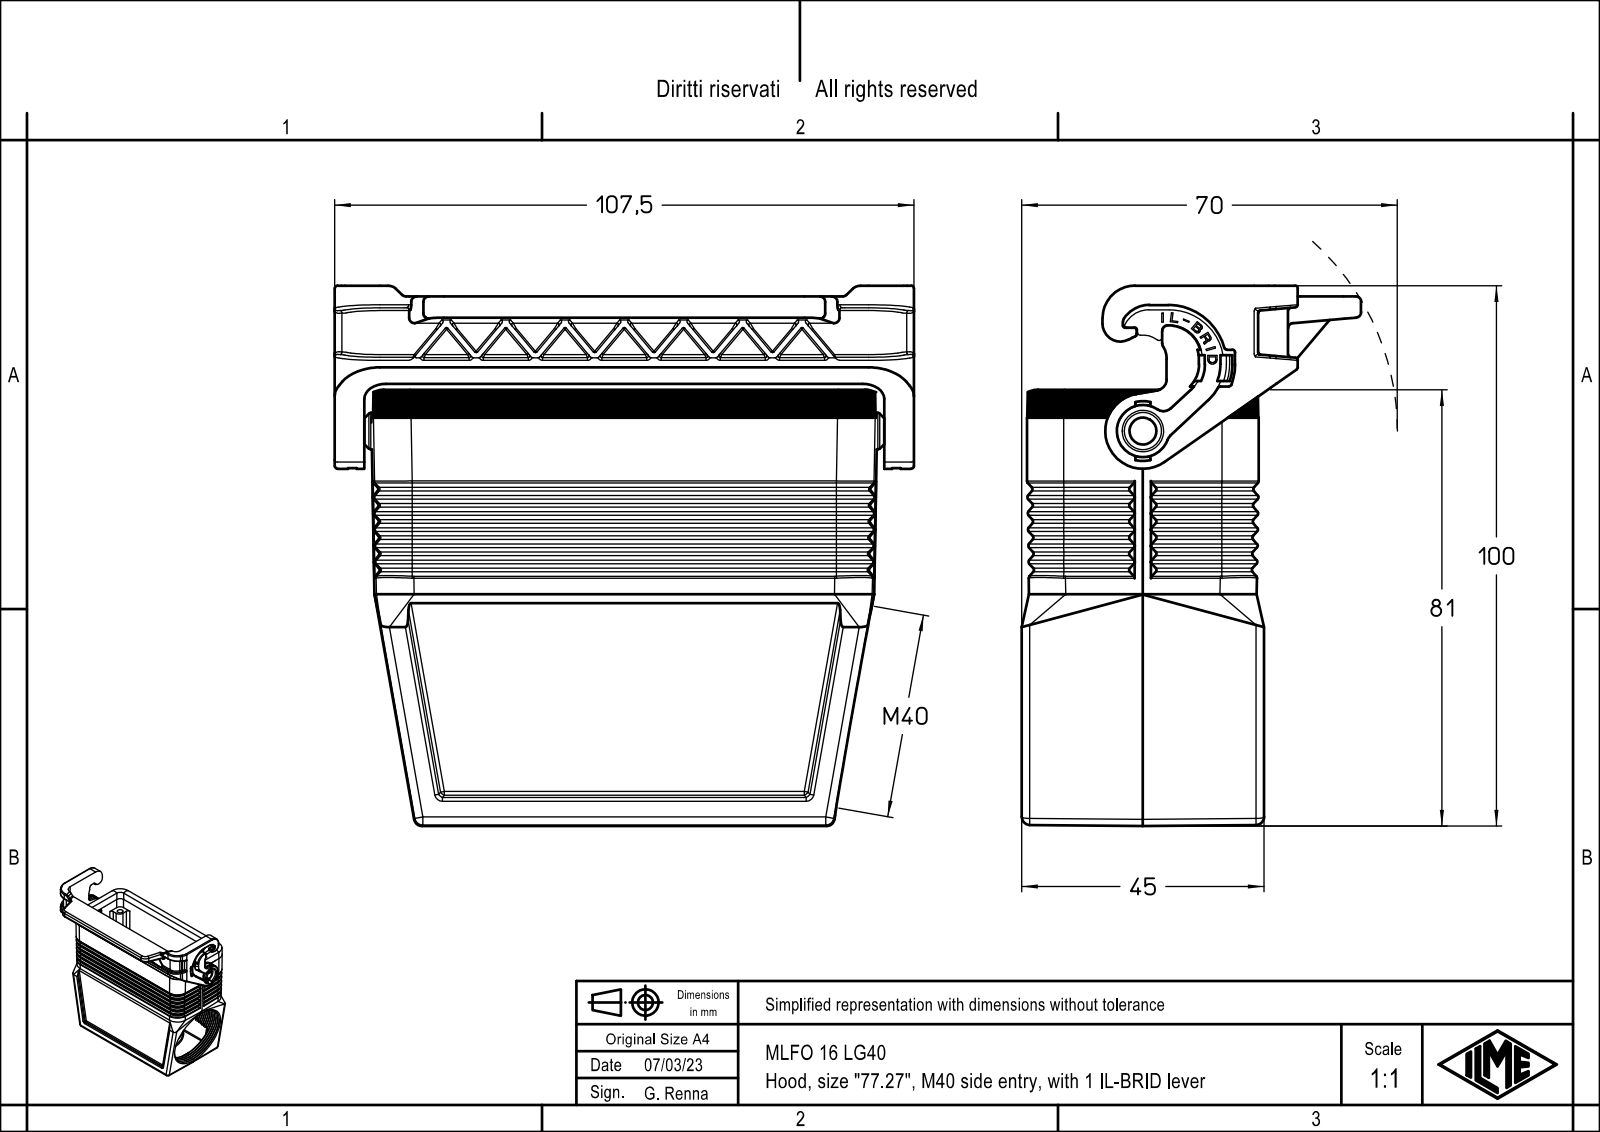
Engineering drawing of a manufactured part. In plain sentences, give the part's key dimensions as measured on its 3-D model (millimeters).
The part is named "MLFO 16 LG40". Its 3-D file was written by "Creo Elements/Direct Modeling 20.1B 02-Apr-2019 (C) Parametric Technology GmbH (AUTOMOTIVE_DESIGN)". It is 1 solid with 1412 faces: 788 planar, 363 cylindrical and 261 other. Overall it measures 107.5 by 100.25 by 63 millimeters. Its volume is 105 253 cubic millimeters and its surface area 58 716 square millimeters. Round holes: 4 of diameter 3, 4 of diameter 3.5, 1 of diameter 3.25, 1 of diameter 5.4, 1 of diameter 7.7. Round bosses or shafts: 1 of diameter 6.9, 1 of diameter 6.8, 1 of diameter 5.2, 1 of diameter 3.2. Partial cylindrical surfaces (rounded edges, fillets, slot ends): 80 of radius 0.5, 27 of radius 0.1, 23 of radius 1.5, 15 of radius 0.2, 15 of radius 1, 14 of radius 7, 13 of radius 0.33, 12 of radius 3. The main face-to-face distances are 3.75, 39.25, 35.5, 43, 2, 7, 46.25, 3.25, 42.5, 1. The hole center spacings are 27, 77.5, 82.07.
